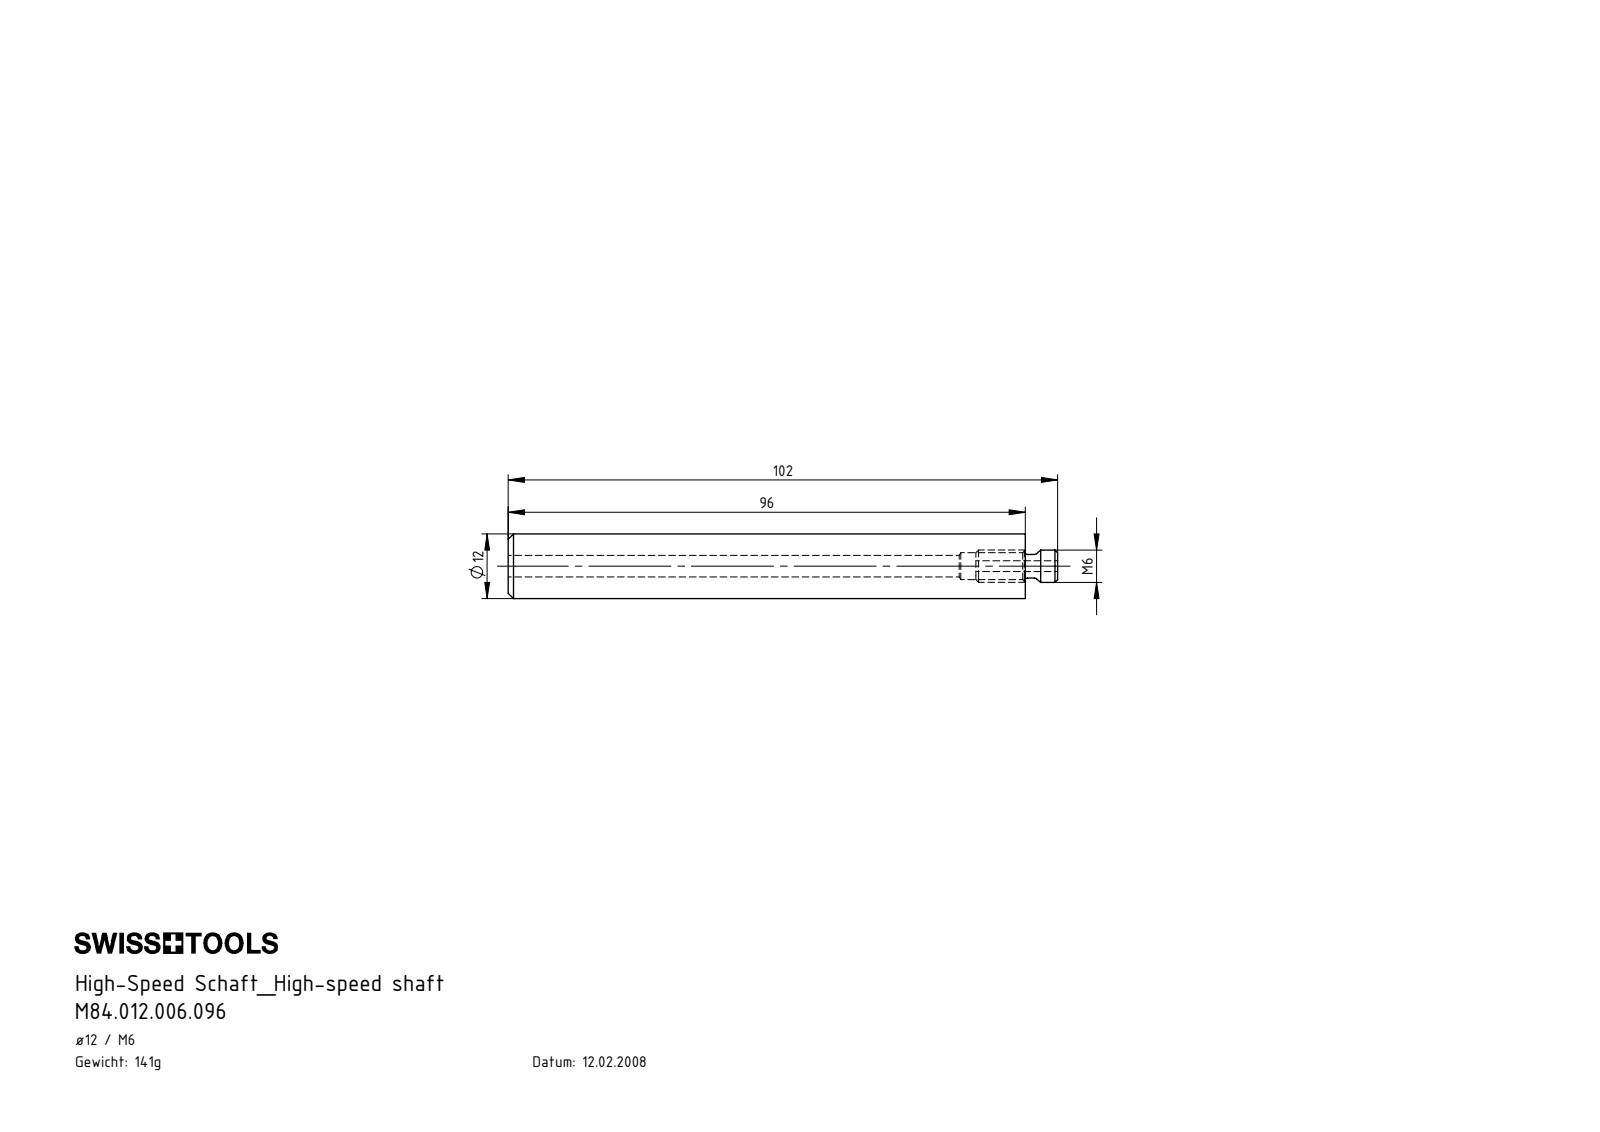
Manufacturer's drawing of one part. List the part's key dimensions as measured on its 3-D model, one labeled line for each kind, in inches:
Part name (STEP PRODUCT): HM1-U12.001.096_A; U12.HS6.K01.096; HM1-BG1.006.015_A
STEP written by: SolidWorks 2017 (AUTOMOTIVE_DESIGN)
Units: inches
Bodies: 2 solids, 20 faces (5 planar, 7 cylindrical, 8 other)
Overall size (bounding box): 4.016 × 0.472 × 0.472
Volume: 0.604 in³ · Surface area: 8.457 in²
Round holes (diameter × count): ⌀0.079 ×1, ⌀0.157 ×1, ⌀0.197 ×1
Round bosses / shafts (diameter × count): ⌀0.472 ×1, ⌀0.236 ×1, ⌀0.173 ×1
Main face-to-face distances: 3.78, 3.417, 0.362, 4.016, 0.598, 0.236, 3.772, 0.354, 0.244
